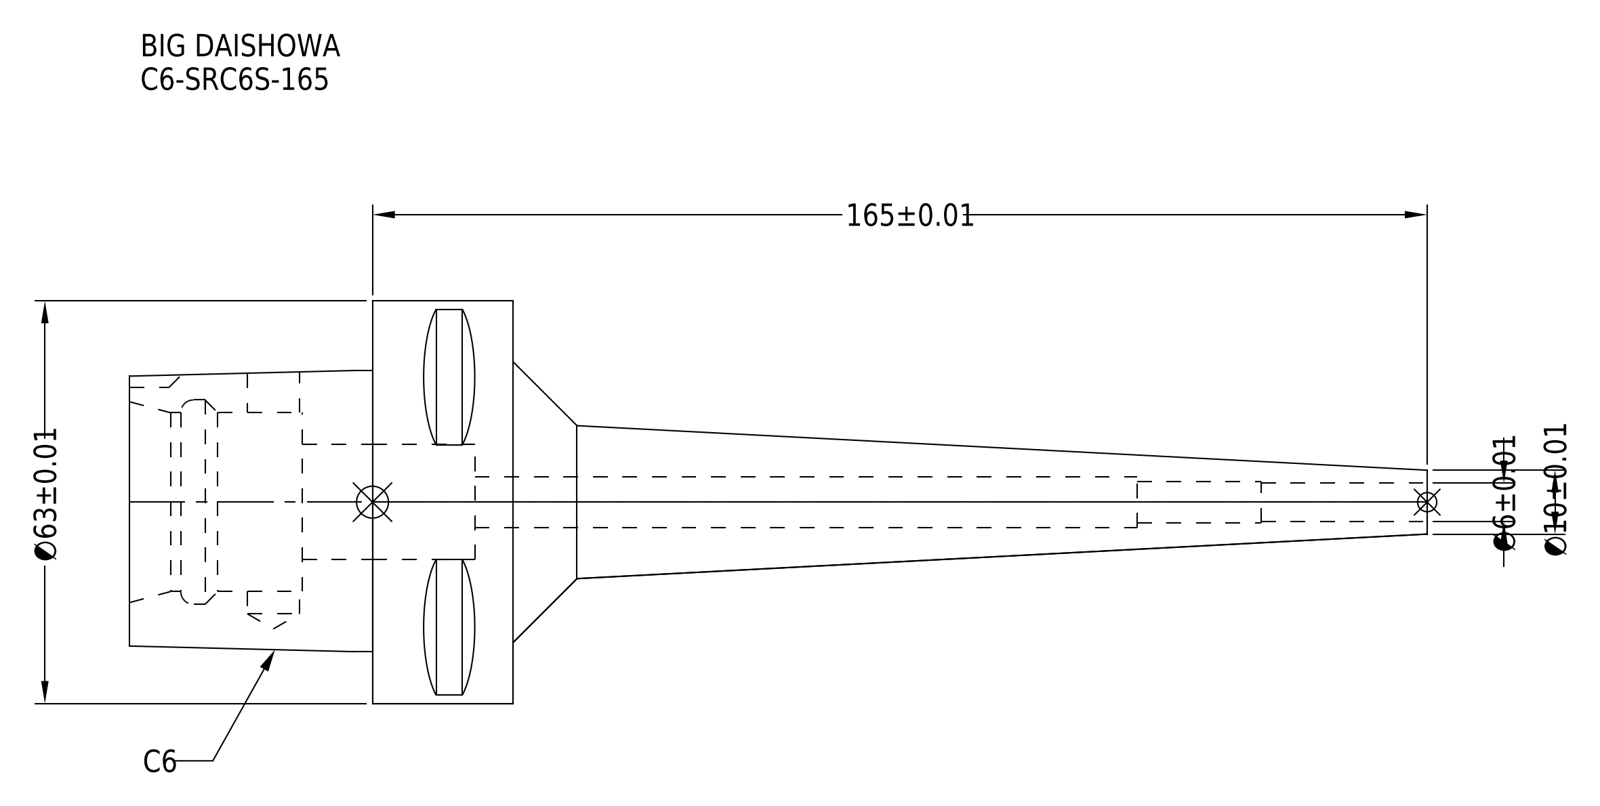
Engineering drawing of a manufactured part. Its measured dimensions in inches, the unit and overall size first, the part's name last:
Units: inches
Overall size (bounding box): 7.992 × 2.48 × 2.48
Round holes (diameter × count): ⌀0.236 ×1, ⌀0.256 ×1, ⌀0.315 ×1, ⌀0.319 ×1, ⌀0.709 ×1, ⌀1.102 ×1, ⌀1.26 ×1
Round bosses / shafts (diameter × count): ⌀2.48 ×1
Partial cylindrical surfaces — rounded edges, fillets, slot ends (radius × count): R0.197 ×1
Main face-to-face distances: 0.866, 1.063, 2.362, 1.496, 1.299, 0.433, 0.98, 2.181, 0.236, 0.63
Volume: 7.999 in³ · Surface area: 47.67 in²
Bodies: 1 solid, 65 faces (30 planar, 21 cylindrical, 14 other)
Part name (STEP PRODUCT): C6-SRC6S-165
STEP written by: CREO PARAMETRIC BY PTC INC, 2016380 (AUTOMOTIVE_DESIGN)
